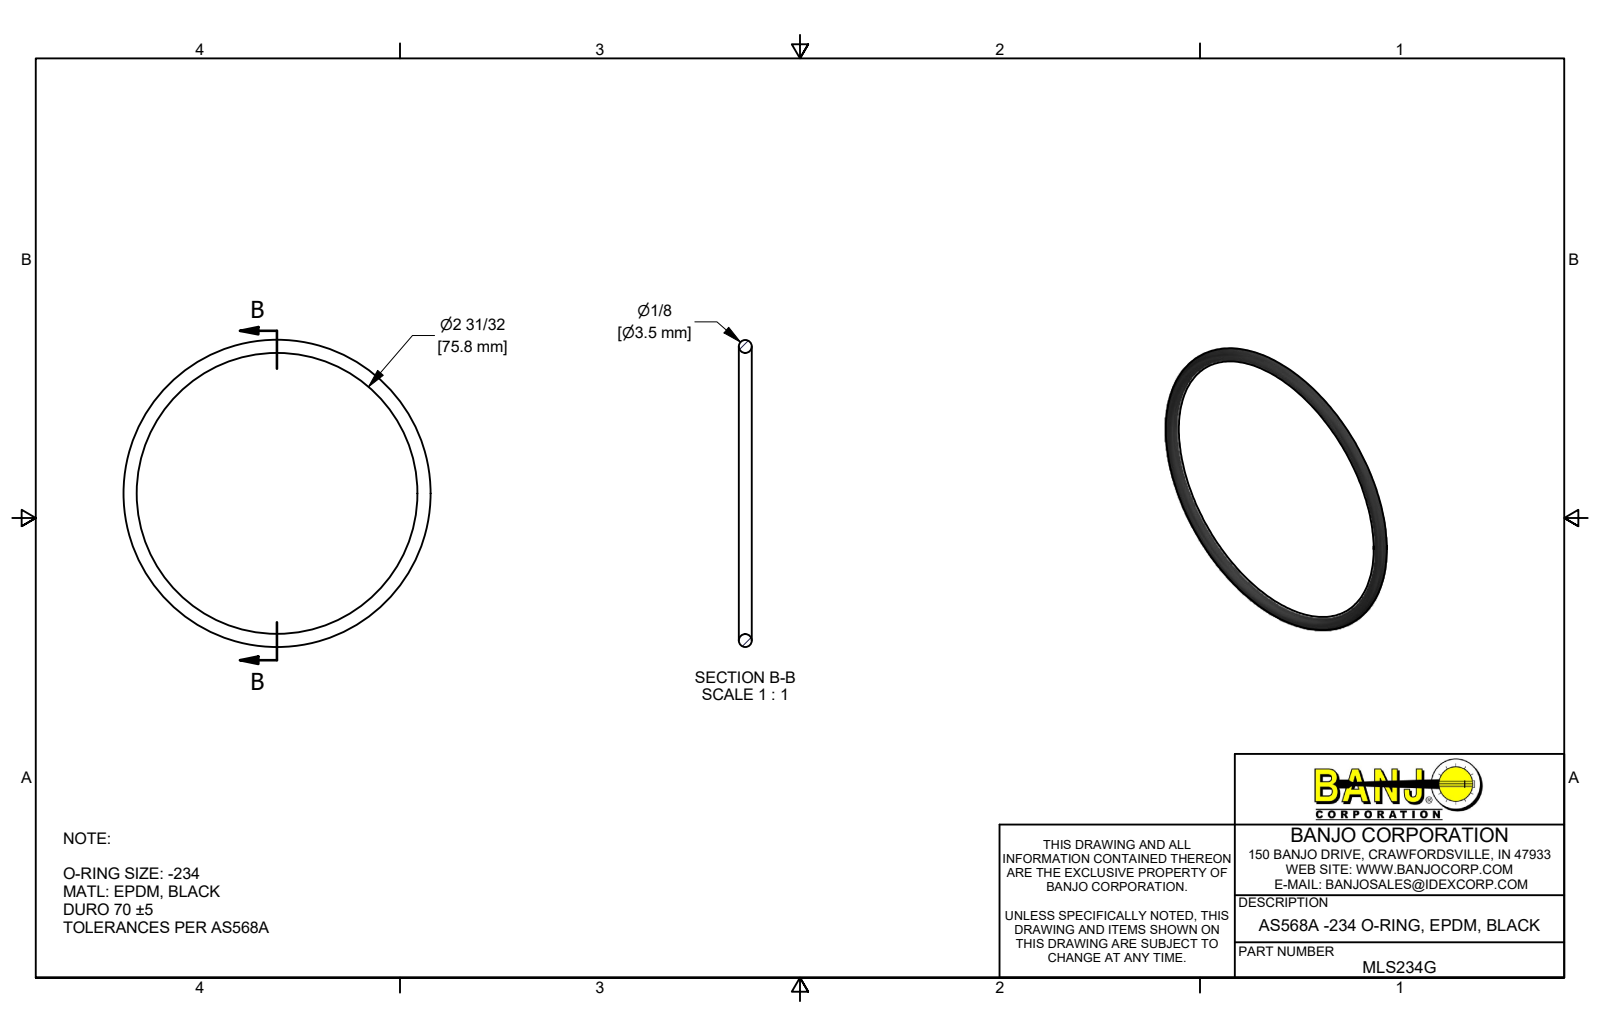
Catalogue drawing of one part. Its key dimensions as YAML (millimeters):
part_name: "MLS234G"
step_written_by: "Autodesk Inventor 2019 (AUTOMOTIVE_DESIGN)"
units: millimeters
bodies: {solids: 1, faces: 1, planar: 0, cylindrical: 0, other: 1}
overall_size: [82.9, 82.9, 3.5]
volume: 2440
surface_area: 2764
